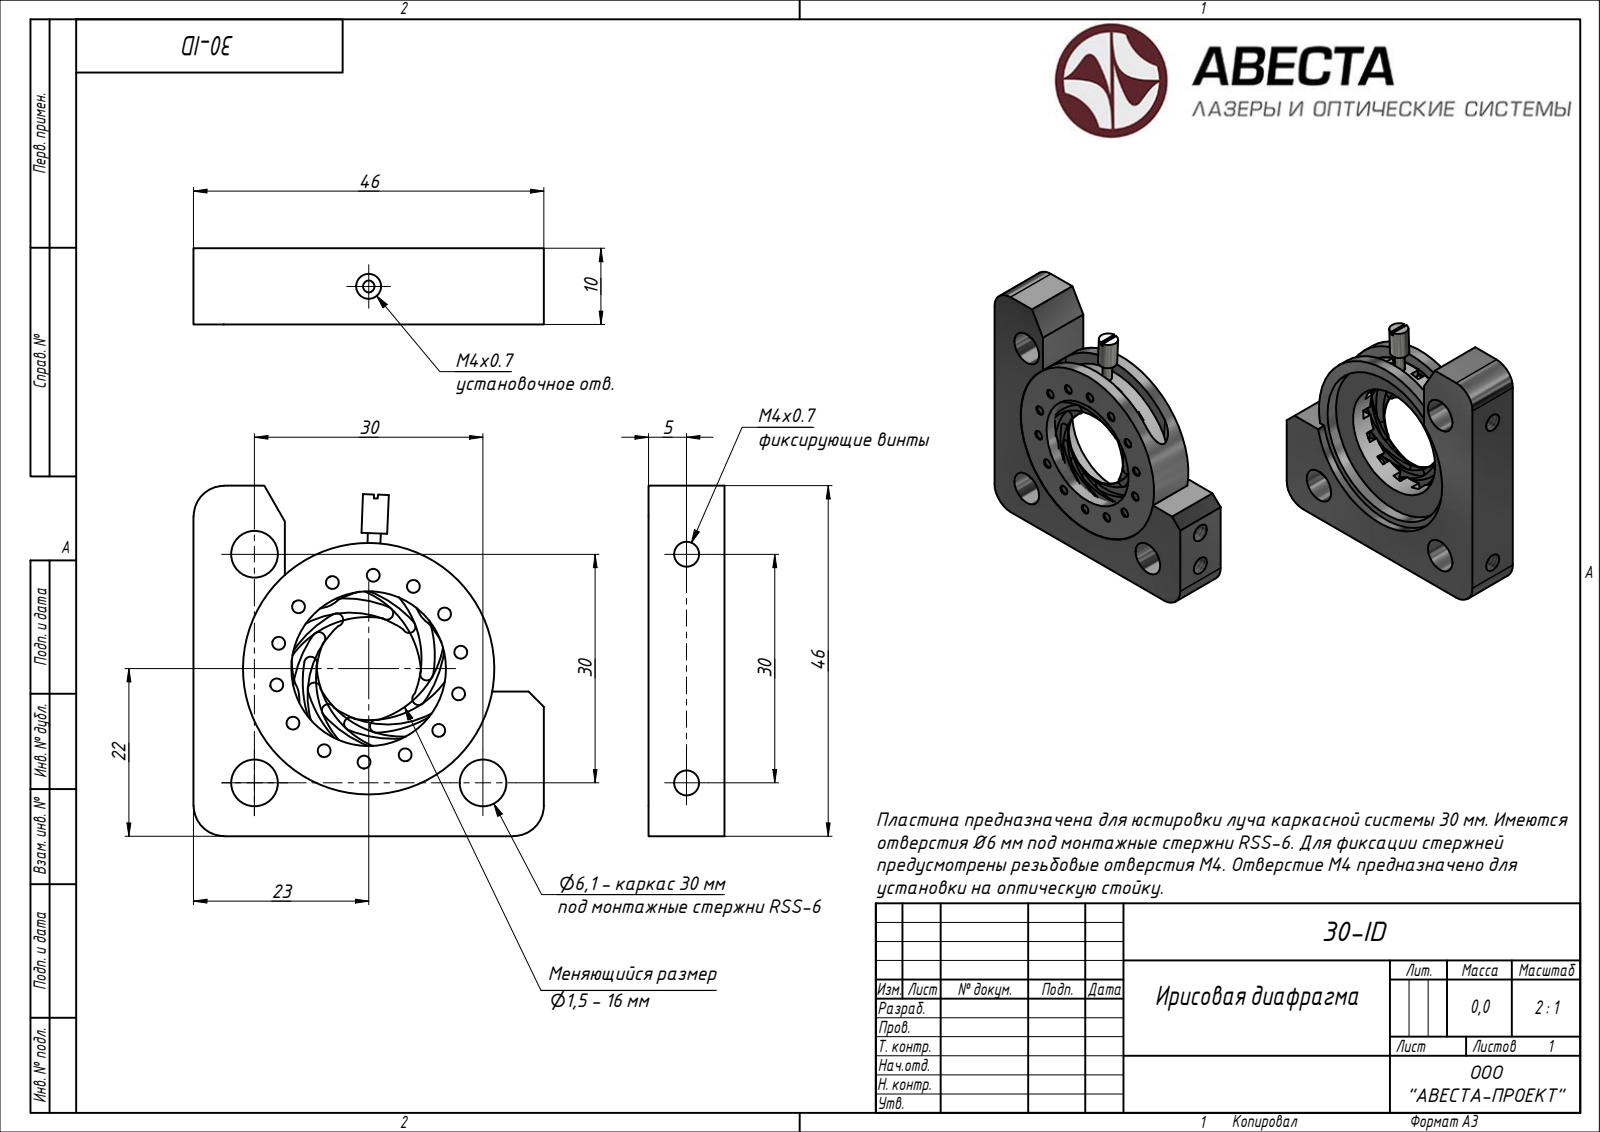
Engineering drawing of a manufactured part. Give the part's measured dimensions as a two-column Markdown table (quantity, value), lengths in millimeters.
| quantity | value |
| --- | --- |
| STEP written by | ST-DEVELOPER v15 (AUTOMOTIVE_DESIGN) |
| units | millimeters |
| bodies | 18 solids, 404 faces (167 planar, 0 cylindrical, 237 other) |
| overall size | 46 × 46 × 10 |
| volume | 10 398 mm³ |
| surface area | 10 548 mm² |
| main face-to-face distances | 7.83, 8, 10, 2.17, 2, 9.96, 2.13, 1.96, 4.23, 3.6 |
